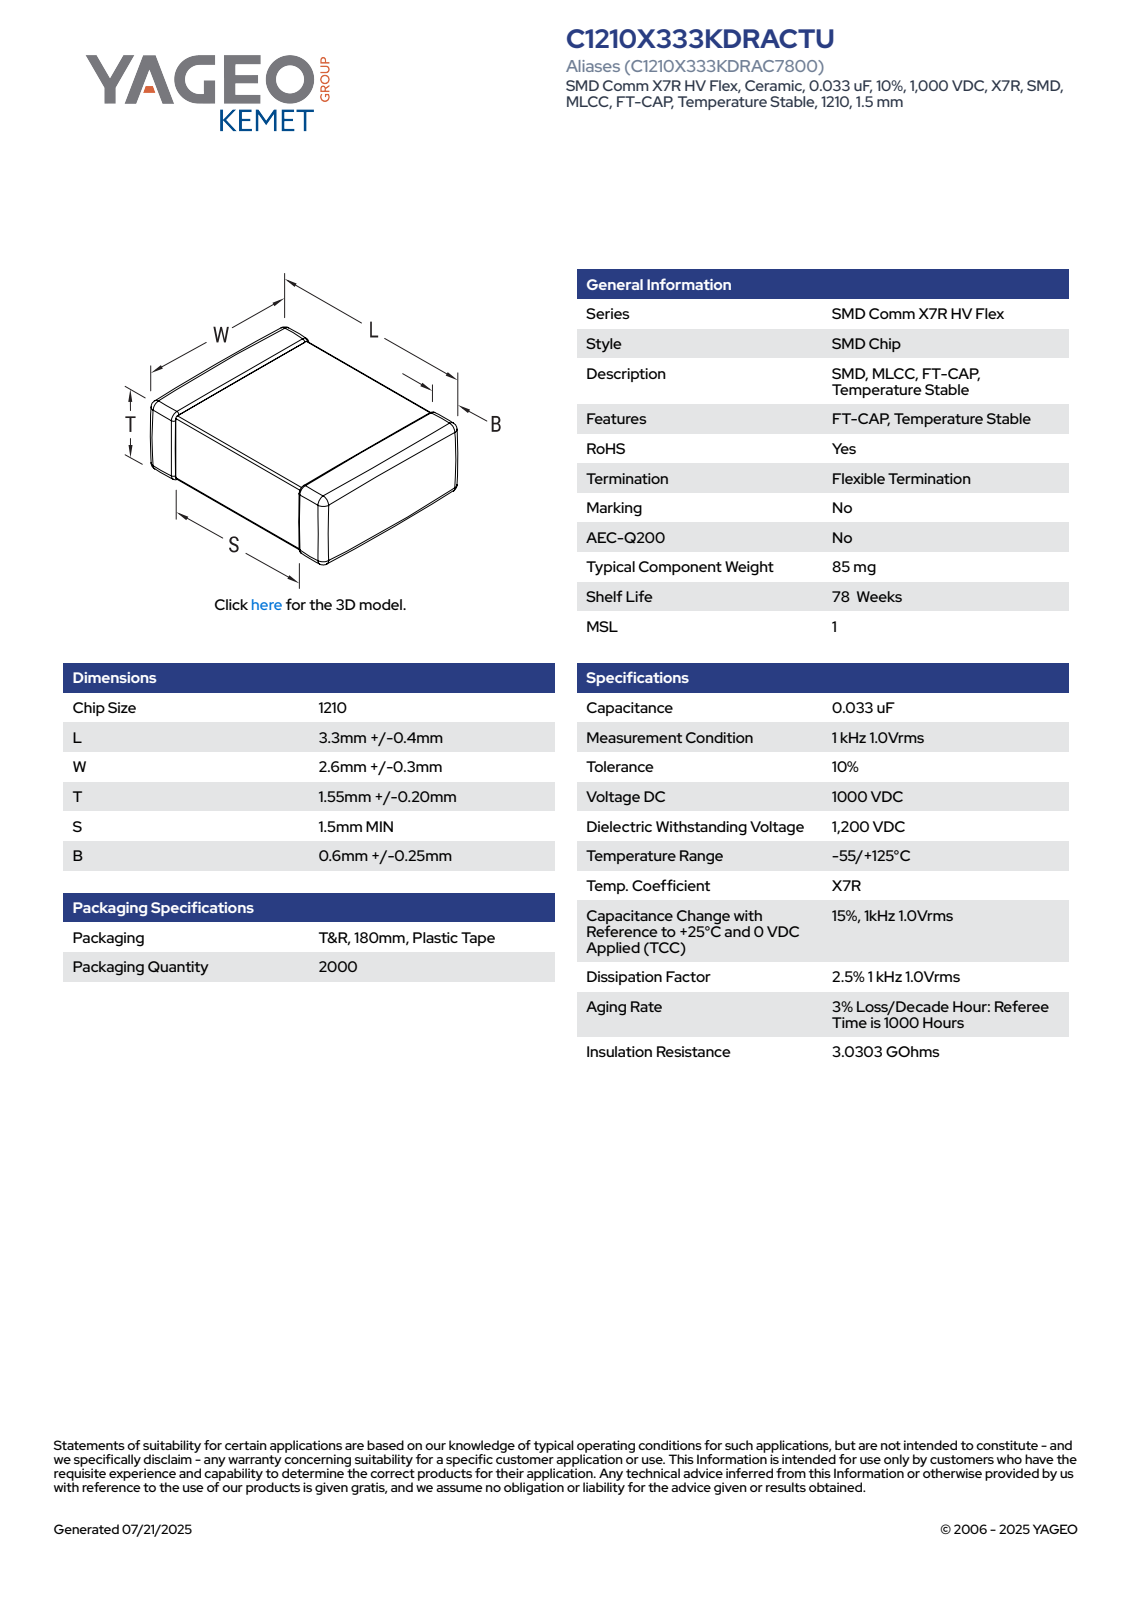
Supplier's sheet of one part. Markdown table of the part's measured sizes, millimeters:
| quantity | value |
| --- | --- |
| part name | CCS_CCSTD_1210_L3.7W2.9T1.75B0.6 |
| STEP written by | SolidWorks 2021 (AUTOMOTIVE_DESIGN) |
| units | millimeters |
| bodies | 4 solids, 125 faces (71 planar, 38 cylindrical, 16 other) |
| overall size | 3.7 × 2.9 × 1.75 |
| volume | 18 mm³ |
| surface area | 44 mm² |
| main face-to-face distances | 1.69, 1.63, 2.84, 3.7, 1.75, 2.78, 2.9, 0.43, 1.57, 2.13 |
